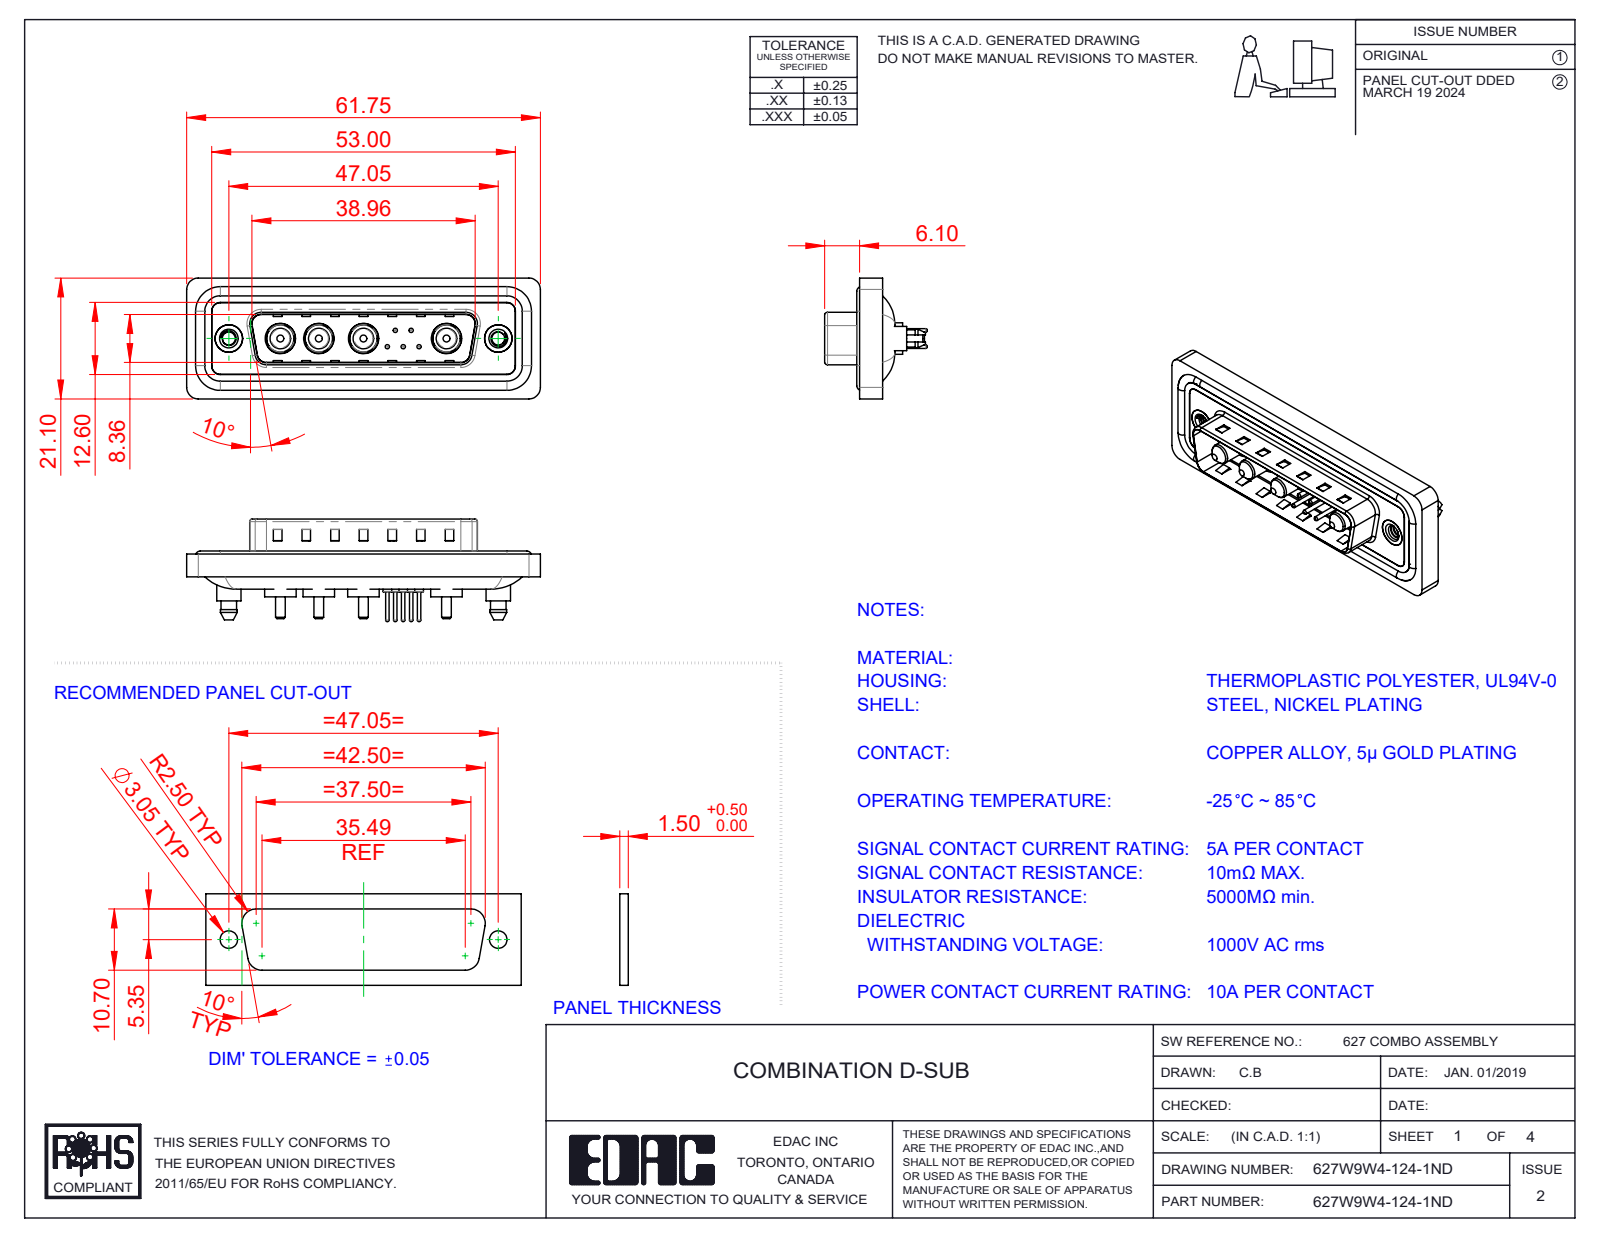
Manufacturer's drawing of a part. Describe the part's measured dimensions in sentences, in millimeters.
The part is named "627Combo Contact Row 1_24; 627Combo Threaded Boardlock_5; 627Combo Waterproof Housing_25 Contacts; 627Combo Housing_9W4 (+6 more)". Its 3-D file was written by "SolidWorks 2023 (CONFIG_CONTROL_DESIGN)". It is 20 solids with 882 faces: 300 planar, 374 cylindrical and 208 other. Overall it measures 61.75 by 21.1 by 17.9 millimeters. Its volume is 7 480 cubic millimeters and its surface area 12 121 square millimeters. Round holes: 5 of diameter 0.75, 5 of diameter 1.6, 5 of diameter 2, 4 of diameter 4.85, 4 of diameter 5.3, 2 of diameter 2.26, 2 of diameter 4, 2 of diameter 4.8, 2 of diameter 5. Round bosses or shafts: 5 of diameter 1.5, 5 of diameter 0.6, 4 of diameter 5.5, 4 of diameter 5.2, 4 of diameter 4.75, 4 of diameter 3.75, 4 of diameter 3.6, 4 of diameter 1.7. Partial cylindrical surfaces (rounded edges, fillets, slot ends): 24 of radius 1.5, 18 of radius 2, 10 of radius 1.6, 8 of radius 0.5, 4 of radius 0.25, 4 of radius 0.6, 4 of radius 0.65, 4 of radius 0.9. The main face-to-face distances are 0.4, 1.5, 1.1, 0.5, 1.6, 3.1, 2.9, 0.82, 9.58, 5.65. The hole center spacings are 3.16, 2.77, 5.04, 14.51, 2.78, 4.4, 4.41, 5.
